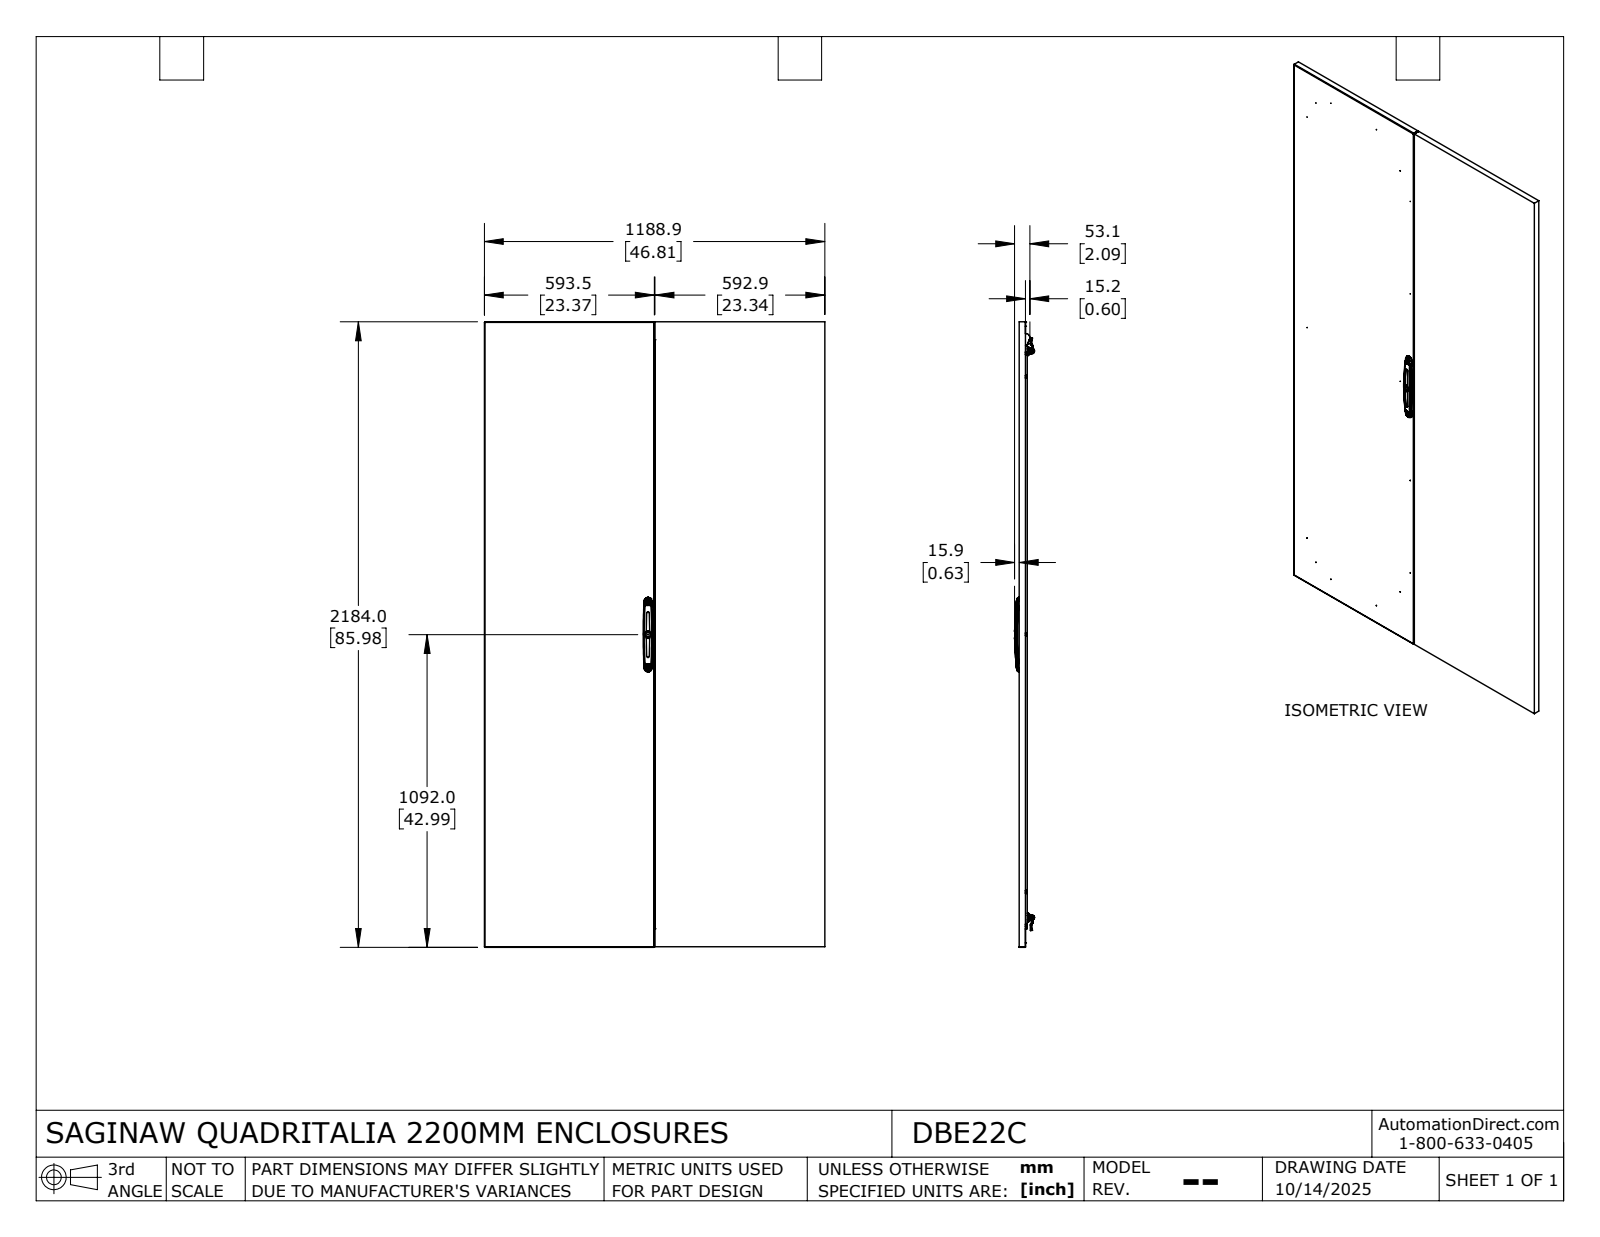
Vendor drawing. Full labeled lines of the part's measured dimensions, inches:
Part name (STEP PRODUCT): DBE22C
STEP written by: SolidWorks 2024 (AUTOMOTIVE_DESIGN)
Units: inches
Bodies: 2 solids, 2741 faces (1137 planar, 834 cylindrical, 770 other)
Overall size (bounding box): 85.984 × 46.809 × 2.608
Volume: 569.8 in³ · Surface area: 10 613 in²
Round holes (diameter × count): ⌀0.167 ×175, ⌀0.167 ×160, ⌀0.354 ×22, ⌀0.039 ×18, ⌀0.354 ×12, ⌀0.193 ×11, ⌀0.194 ×8, ⌀0.134 ×2, ⌀0.169 ×2, ⌀0.177 ×2, ⌀0.194 ×2, ⌀0.205 ×2
Round bosses / shafts (diameter × count): ⌀0.276 ×12, ⌀0.236 ×12, ⌀0.283 ×10, ⌀1.101 ×2, ⌀0.779 ×2, ⌀0.598 ×2, ⌀0.472 ×2, ⌀0.275 ×2
Partial cylindrical surfaces — rounded edges, fillets, slot ends (radius × count): R0.039 ×26, R0.177 ×20, R0.227 ×11, R0.157 ×10, R0.227 ×10, R0.02 ×9, R0.008 ×8, R0.138 ×8
Main face-to-face distances: 0.079, 0.059, 0.728, 0.787, 1.042, 0.787, 0.865, 1.121, 0.256, 0.866
Hole centre spacings: 0.984, 1.969, 2.953, 3.937, 4.094, 6.542, 14.256, 35.433
